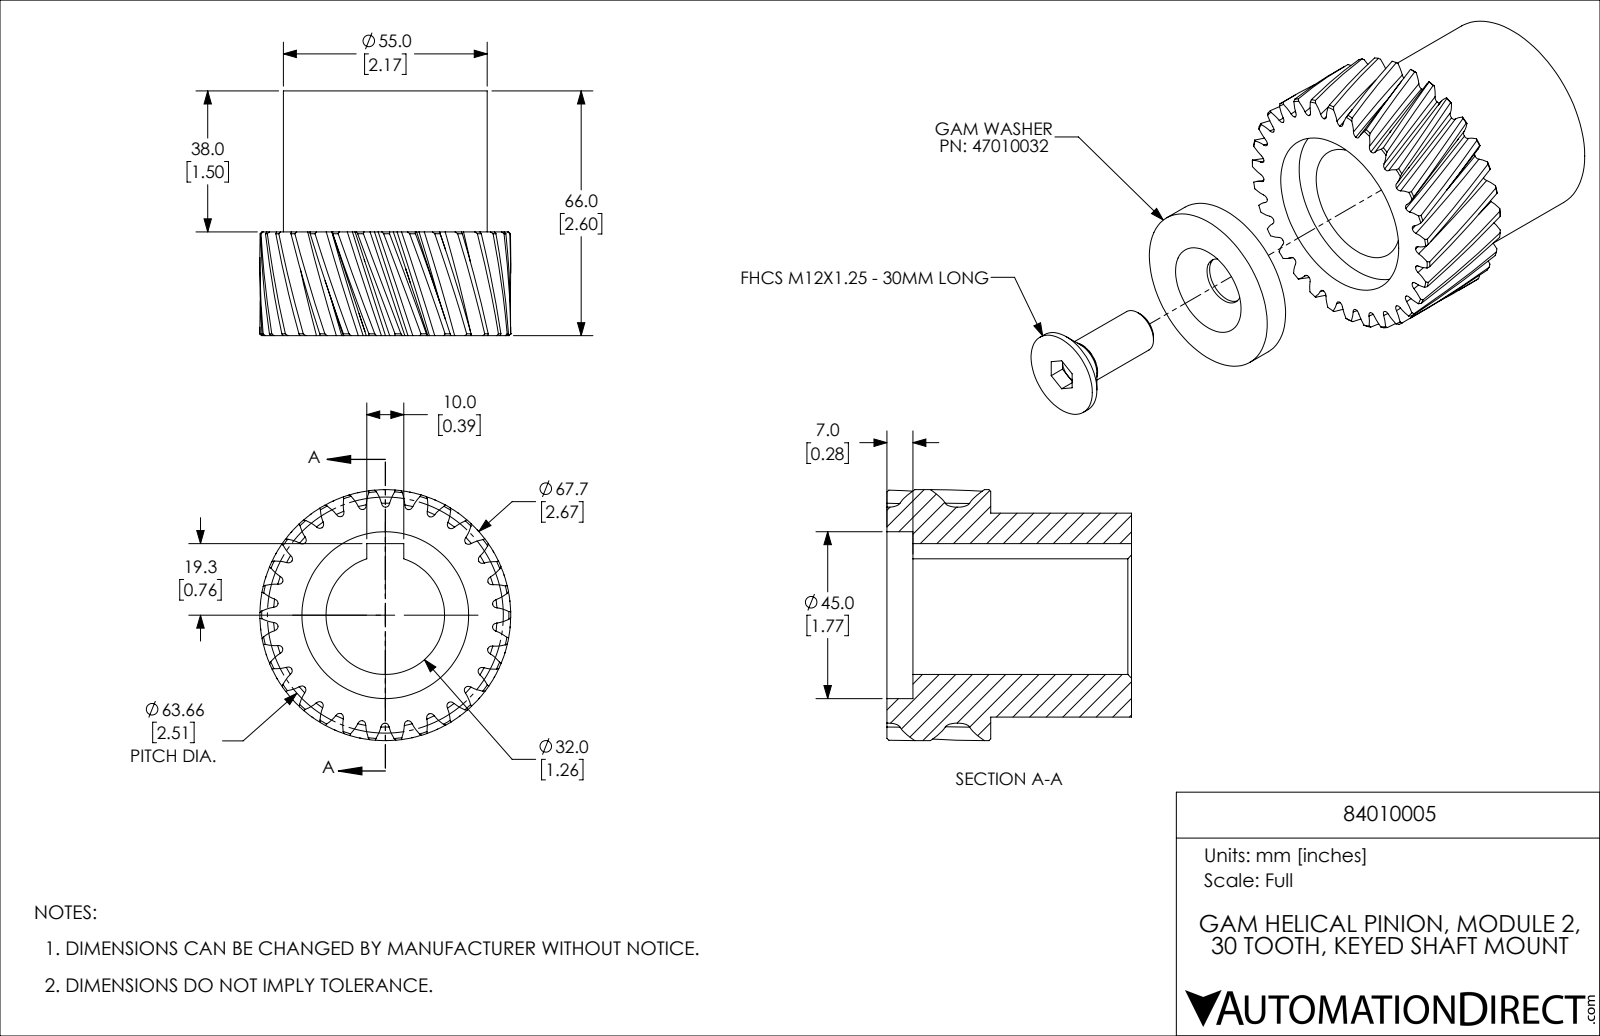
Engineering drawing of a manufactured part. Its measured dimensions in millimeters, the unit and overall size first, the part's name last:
Units: millimetres
Overall size (bounding box): 67.7 × 67.7 × 66
Round holes (diameter × count): ⌀13 ×1, ⌀32 ×1, ⌀45 ×1
Round bosses / shafts (diameter × count): ⌀67.7 ×1, ⌀55 ×1, ⌀23.4 ×1, ⌀12 ×1
Main face-to-face distances: 7, 66, 59, 28, 21, 38, 10, 30, 23, 2
Volume: 131 406 mm³ · Surface area: 35 837 mm²
Bodies: 3 solids, 264 faces (23 planar, 47 cylindrical, 194 other)
Part name (STEP PRODUCT): 84010005
STEP written by: SolidWorks 2019 (CONFIG_CONTROL_DESIGN)
